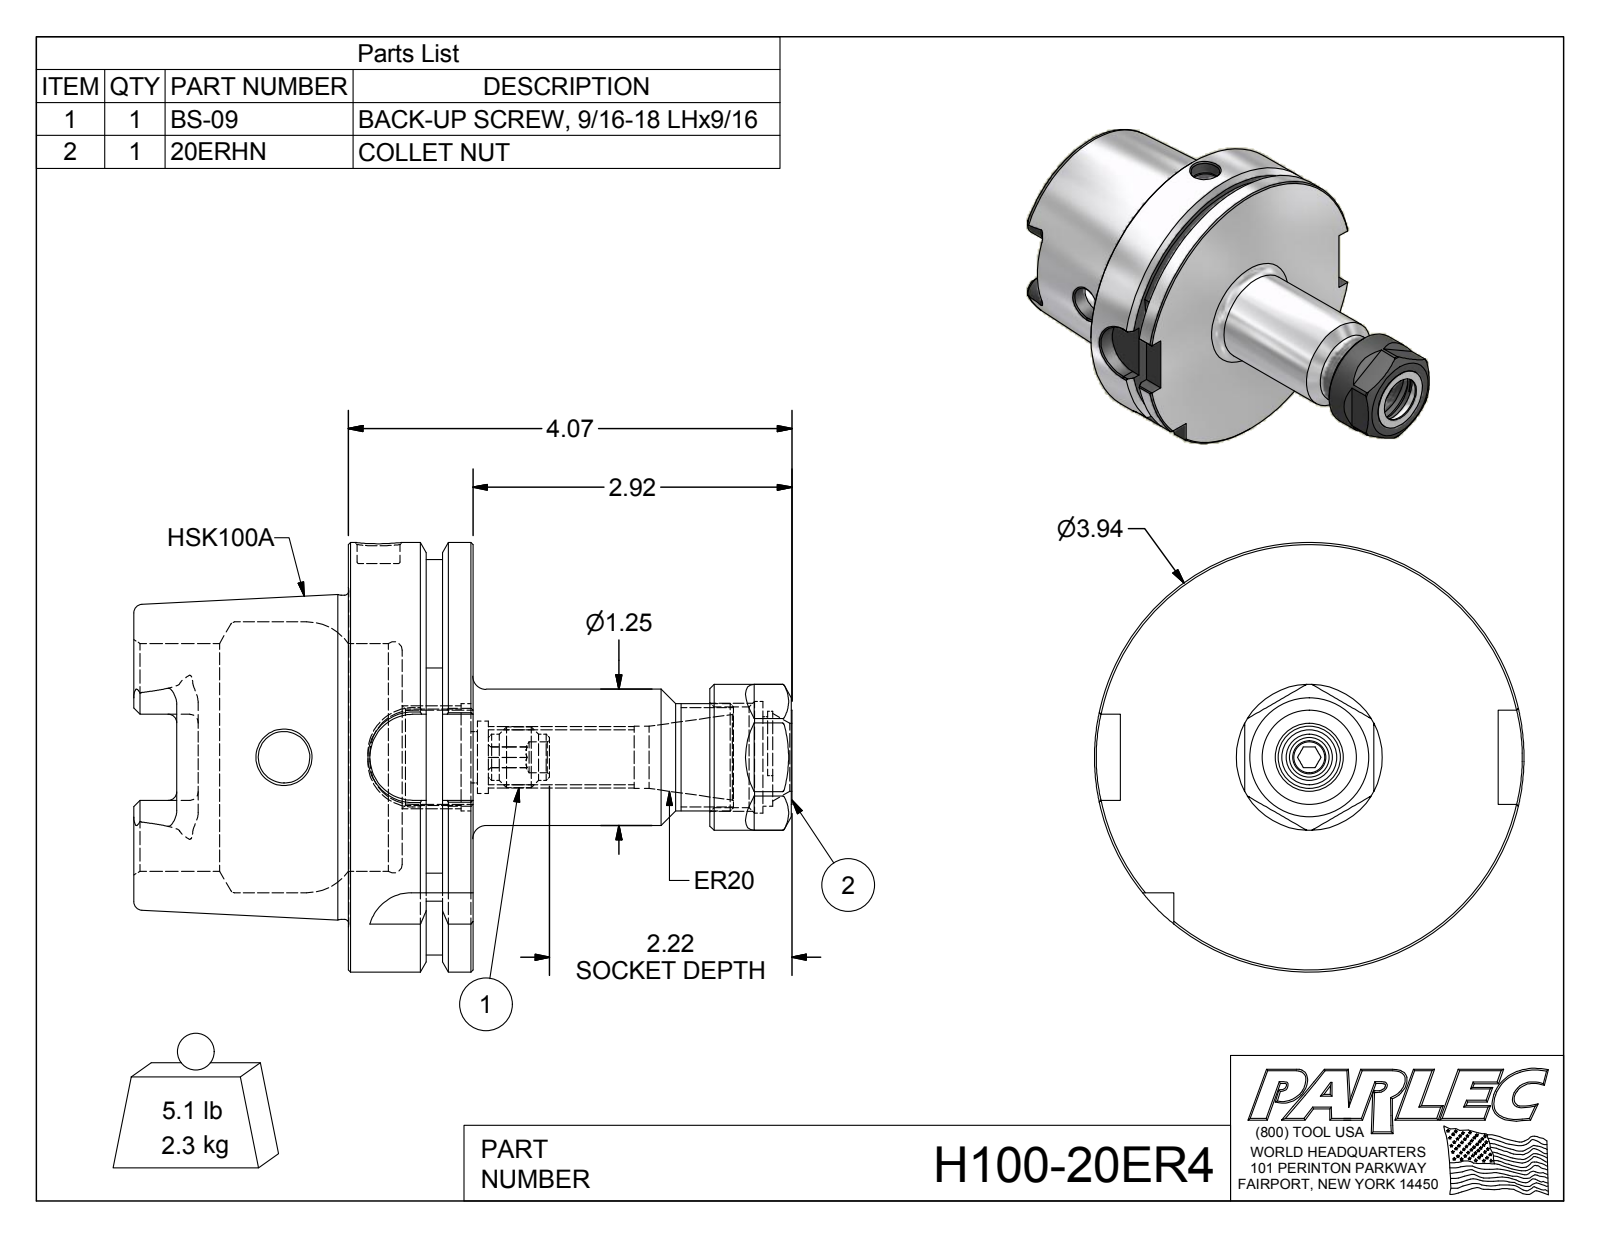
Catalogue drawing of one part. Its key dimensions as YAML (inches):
part_name: "H100-20ER4; H100-20ER4-1; BS-09; 20ERHN"
step_written_by: "Autodesk Inventor 2012 (AUTOMOTIVE_DESIGN)"
units: inches
bodies: {solids: 3, faces: 192, planar: 78, cylindrical: 48, other: 66}
overall_size: [6.034, 3.937, 3.937]
volume: 18.11
surface_area: 98.63
round_holes:
  - {diameter: 0.472, count: 2}
  - {diameter: 0.281, count: 1}
  - {diameter: 0.394, count: 1}
  - {diameter: 0.472, count: 1}
  - {diameter: 0.502, count: 1}
  - {diameter: 0.57, count: 1}
  - {diameter: 0.62, count: 1}
  - {diameter: 0.663, count: 1}
  - {diameter: 0.82, count: 1}
  - {diameter: 0.881, count: 1}
  - {diameter: 0.925, count: 1}
  - {diameter: 0.985, count: 1}
round_bosses_or_shafts:
  - {diameter: 3.937, count: 1}
  - {diameter: 2.967, count: 1}
  - {diameter: 1.339, count: 1}
  - {diameter: 1.25, count: 1}
  - {diameter: 0.984, count: 1}
  - {diameter: 0.86, count: 1}
  - {diameter: 0.555, count: 1}
  - {diameter: 0.422, count: 1}
partial_cylinders:
  - {radius: 0.079, count: 6}
  - {radius: 0.192, count: 4}
  - {radius: 0.394, count: 4}
  - {radius: 0.423, count: 1}
  - {radius: 1.811, count: 1}
face_to_face_distances: [1.142, 0.492, 0.65, 1.969, 2.461, 3.11, 2.83, 0.861, 0.369, 0.28]
hole_center_spacings: [0.037]
